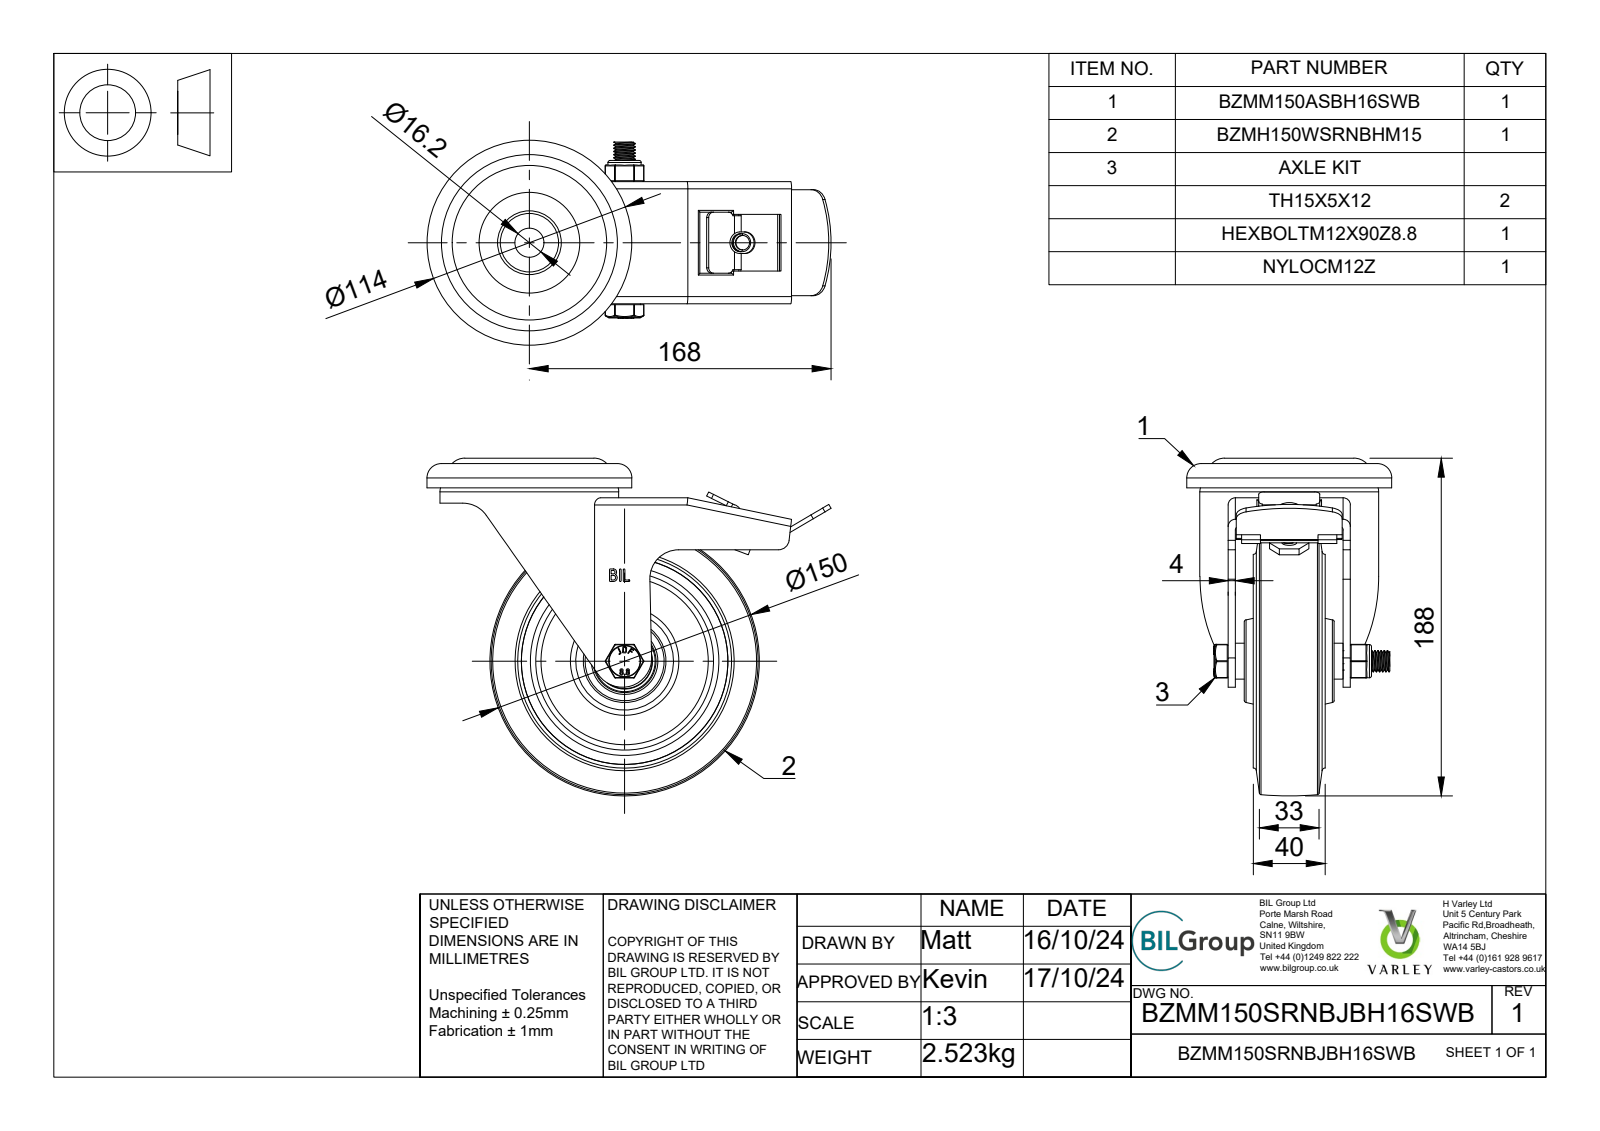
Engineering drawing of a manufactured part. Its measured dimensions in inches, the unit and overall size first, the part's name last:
Units: inches
Overall size (bounding box): 8.858 × 7.402 × 4.488
Round holes (diameter × count): ⌀0.394 ×1, ⌀0.404 ×1, ⌀0.472 ×1, ⌀0.48 ×1, ⌀0.492 ×1, ⌀0.551 ×1, ⌀0.591 ×1, ⌀0.638 ×1, ⌀0.886 ×1, ⌀1.142 ×1, ⌀1.181 ×1, ⌀1.22 ×1
Round bosses / shafts (diameter × count): ⌀4.488 ×1, ⌀3.917 ×1, ⌀2.913 ×1, ⌀1.85 ×1, ⌀1.28 ×1, ⌀1.201 ×1, ⌀0.906 ×1, ⌀0.787 ×1
Partial cylindrical surfaces — rounded edges, fillets, slot ends (radius × count): R0.02 ×24, R0.079 ×8, R0.039 ×6, R0.019 ×4, R0.035 ×4, R0.118 ×4, R0.157 ×4, R0.236 ×3
Main face-to-face distances: 0.157, 1.083, 0.197, 1.28, 0.886, 0.039, 0.394, 1.969, 0.374, 0.217
Volume: 42.76 in³ · Surface area: 397.3 in²
Bodies: 40 solids, 1235 faces (538 planar, 252 cylindrical, 445 other)
Part name (STEP PRODUCT): BZMM150SRNBJBH16SWB v3; BZMM150ASBH16SWB v1; ZINC PLATED, PRESSED STEEL HEAD; ZINC PLATED, PRESSED STEEL FORKS (+8 more)
STEP written by: Autodesk Translation Framework v13.20.0.188 (AUTOMOTIVE_DESIGN)
